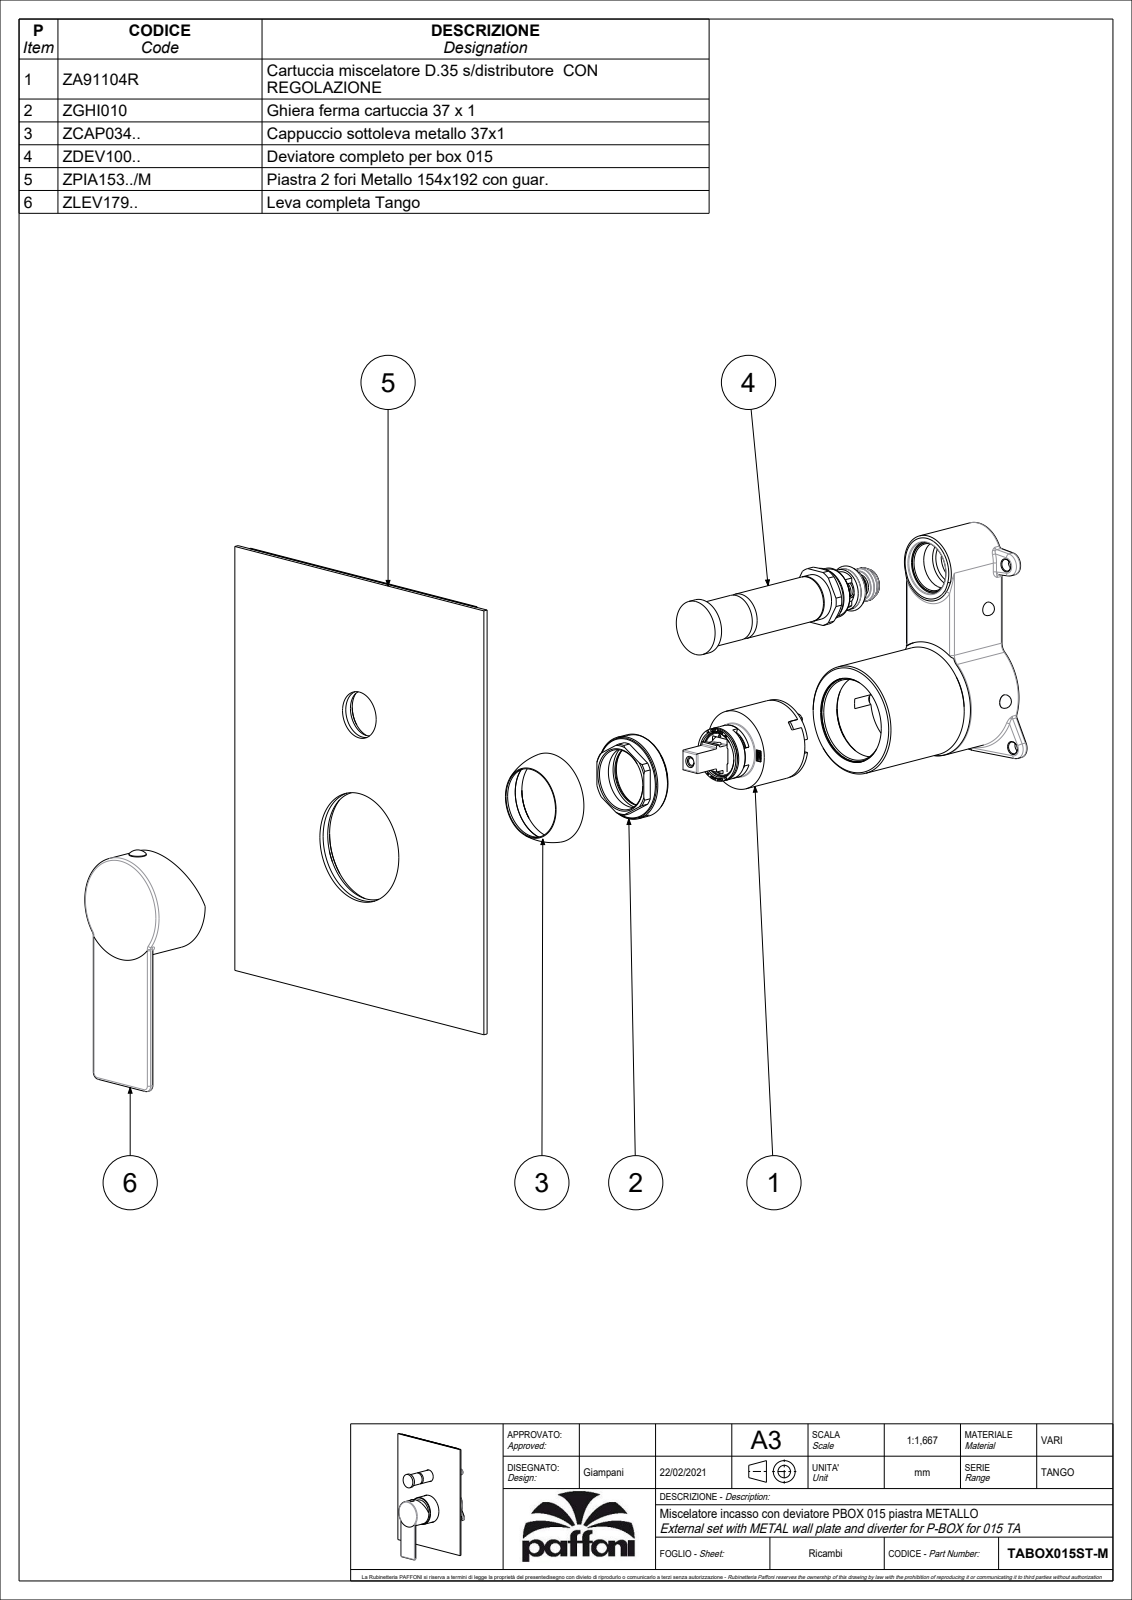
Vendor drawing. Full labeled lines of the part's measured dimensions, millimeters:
Part name (STEP PRODUCT): TABOX015ST-M
STEP written by: CREO PARAMETRIC BY PTC INC, 2020044 (CONFIG_CONTROL_DESIGN)
Units: millimetres
Bodies: 4 solids, 935 faces (577 planar, 207 cylindrical, 151 other)
Overall size (bounding box): 201.75 × 154 × 55.1
Volume: 121 858 mm³ · Surface area: 101 547 mm²
Round holes (diameter × count): ⌀4 ×2, ⌀3 ×1, ⌀3.3 ×1, ⌀5 ×1, ⌀7.1 ×1, ⌀16 ×1, ⌀18.2 ×1, ⌀19.5 ×1, ⌀19.9 ×1, ⌀20.8 ×1, ⌀26.8 ×1, ⌀29 ×1
Round bosses / shafts (diameter × count): ⌀48.1 ×1, ⌀45.5 ×1, ⌀35 ×1, ⌀24 ×1, ⌀23.5 ×1, ⌀23.4 ×1, ⌀21.8 ×1, ⌀20 ×1
Partial cylindrical surfaces — rounded edges, fillets, slot ends (radius × count): R0.15 ×11, R0.5 ×8, R1 ×8, R0.3 ×4, R1.5 ×4, R3 ×2, R2.5 ×1, R3.5 ×1
Main face-to-face distances: 2, 3, 49.6, 54.6, 52.6, 51.6, 0.5, 3.5, 51.1, 49.1
Hole centre spacings: 13, 60
